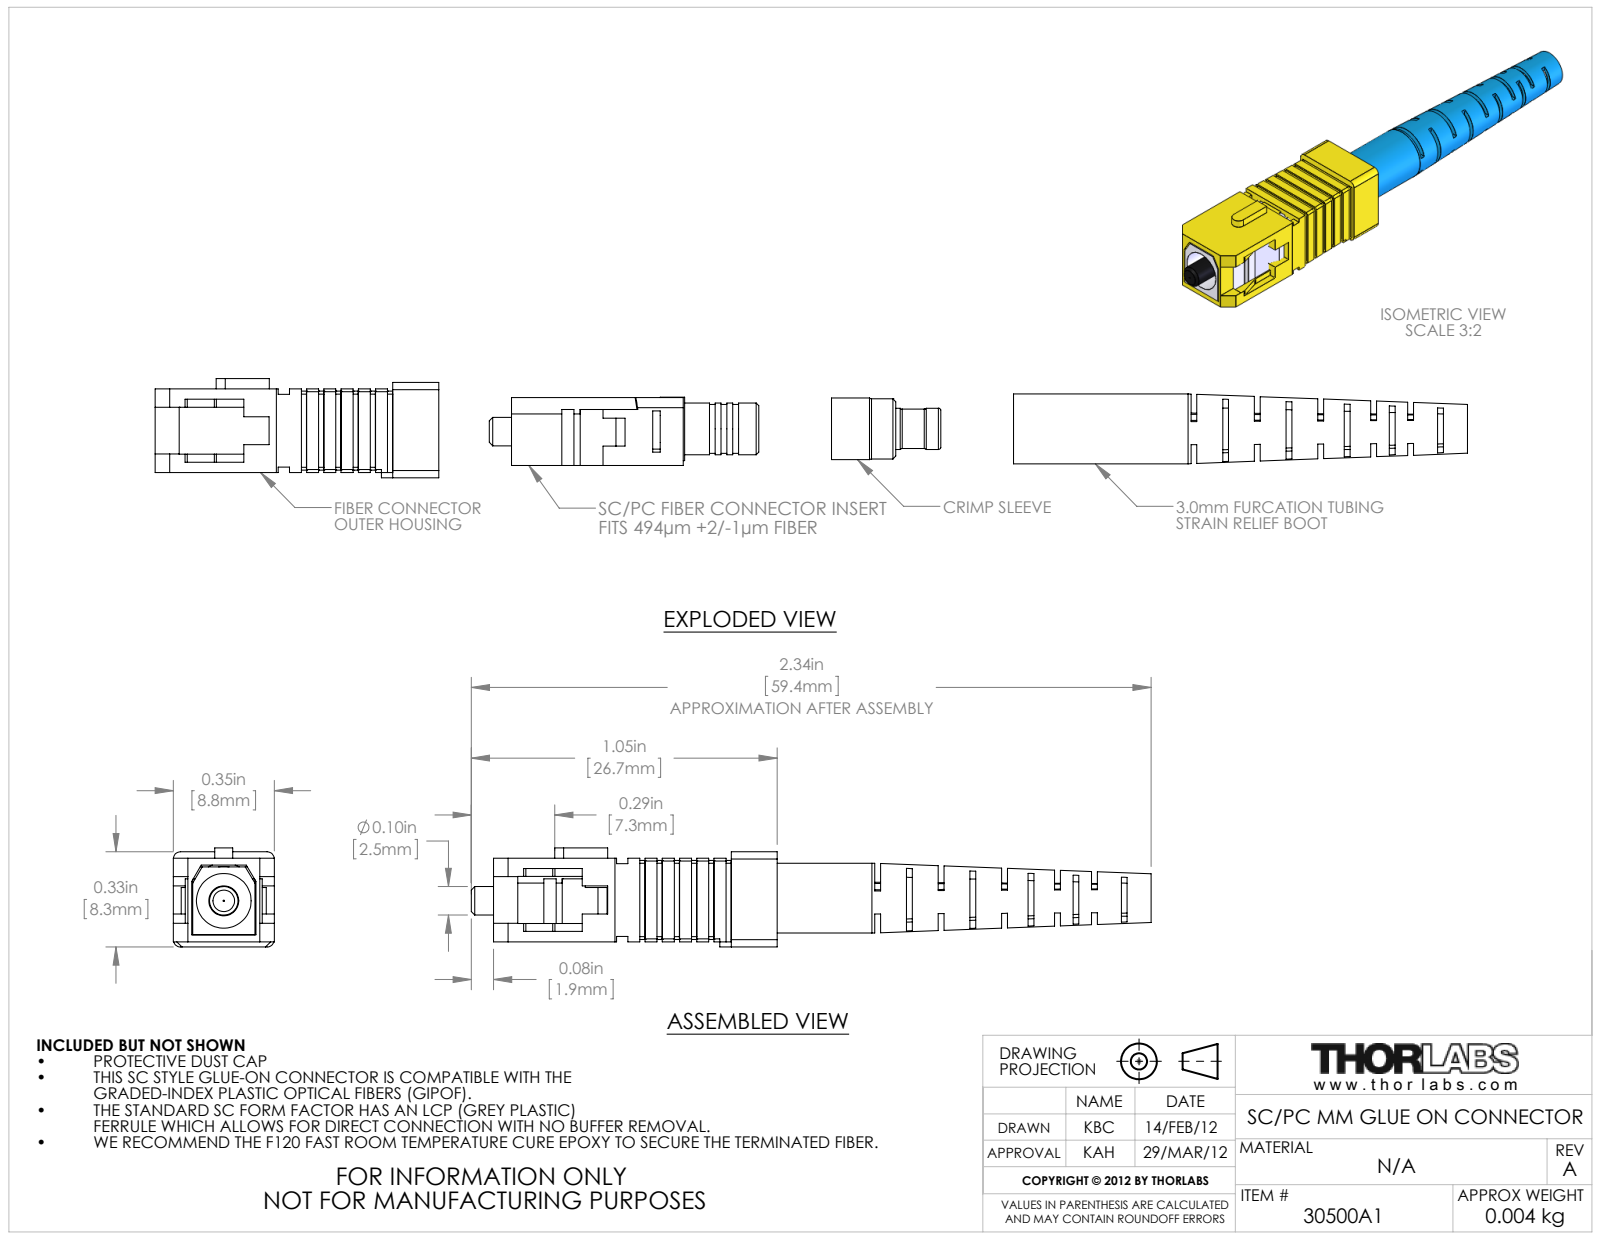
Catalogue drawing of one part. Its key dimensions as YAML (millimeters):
part_name: "19860-E0W"
step_written_by: "SolidWorks 2011 (AUTOMOTIVE_DESIGN)"
units: millimeters
bodies: {solids: 6, faces: 569, planar: 456, cylindrical: 85, other: 28}
overall_size: [59.4, 8.8, 8.7]
volume: 1300
surface_area: 4285
round_holes:
  - {diameter: 2.6, count: 1}
  - {diameter: 2.7, count: 1}
  - {diameter: 3.2, count: 1}
  - {diameter: 3.3, count: 1}
  - {diameter: 4.3, count: 1}
  - {diameter: 4.4, count: 1}
  - {diameter: 4.7, count: 1}
  - {diameter: 4.7, count: 1}
  - {diameter: 4.8, count: 1}
round_bosses_or_shafts:
  - {diameter: 6.1, count: 1}
  - {diameter: 5.5, count: 1}
  - {diameter: 5.4, count: 1}
  - {diameter: 5.3, count: 1}
  - {diameter: 5.1, count: 1}
  - {diameter: 4.5, count: 1}
  - {diameter: 4.3, count: 1}
  - {diameter: 3.6, count: 1}
partial_cylinders:
  - {radius: 0.6, count: 8}
  - {radius: 0.9, count: 4}
  - {radius: 3.2, count: 2}
  - {radius: 0.8, count: 1}
  - {radius: 2.3, count: 1}
face_to_face_distances: [0.6, 6.7, 7.3, 1, 7.8, 7.8, 0.6, 6.8, 1, 0.8]
